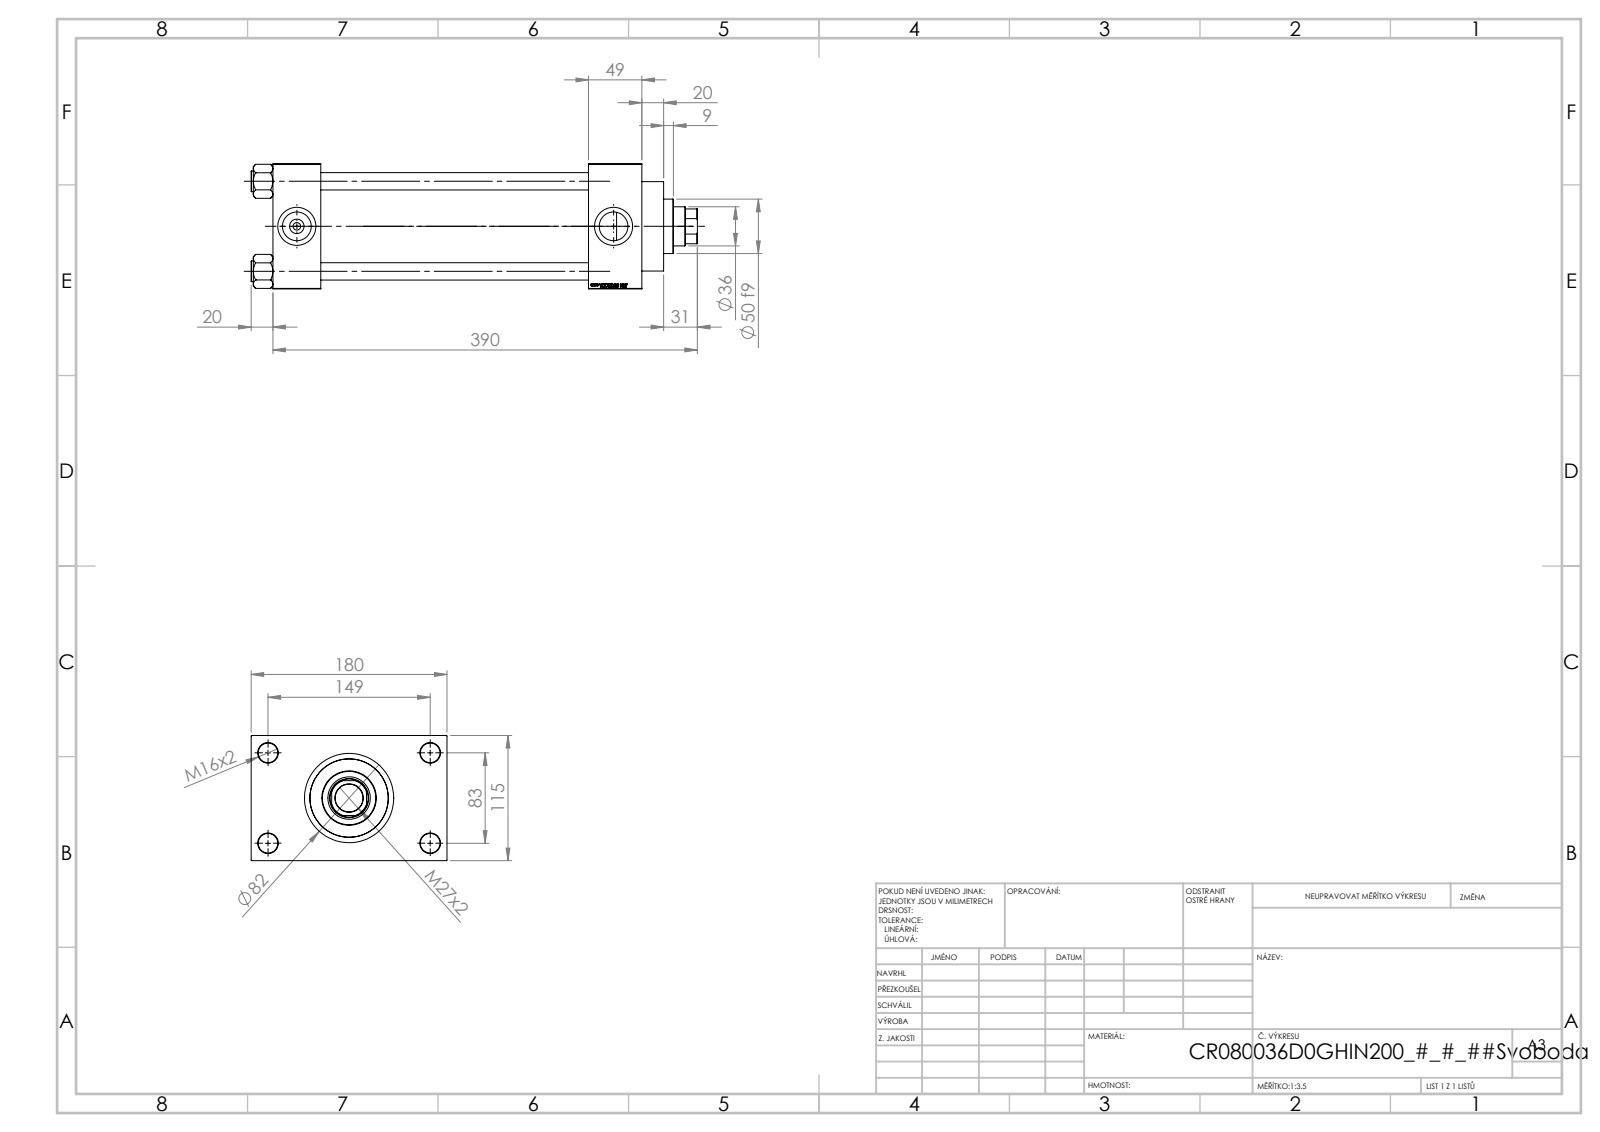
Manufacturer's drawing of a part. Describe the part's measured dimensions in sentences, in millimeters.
The part is named "V215_VC_A; V215CR_D_TYCINKA; NUT_M5_D; V215CR_D_Body (+1 more)". Its 3-D file was written by "SolidWorks 2019 (CONFIG_CONTROL_DESIGN)". It is 11 solids with 1151 faces: 545 planar, 88 cylindrical and 518 other. Overall it measures 410 by 180 by 115 millimeters. Its volume is 2 448 000 cubic millimeters and its surface area 447 014 square millimeters. Round holes: 4 of diameter 16, 4 of diameter 18, 2 of diameter 7, 2 of diameter 26.44, 2 of diameter 35, 1 of diameter 25.5, 1 of diameter 36, 1 of diameter 39, 1 of diameter 61, 1 of diameter 72, 1 of diameter 80. Round bosses or shafts: 4 of diameter 19, 1 of diameter 86, 1 of diameter 82, 1 of diameter 50. Partial cylindrical surfaces (rounded edges, fillets, slot ends): 1 of radius 17.5. The main face-to-face distances are 115, 246, 295, 49, 44, 290, 339, 32.5, 147.5, 180. The hole center spacings are 33.15, 58.48, 82.7, 85.28, 89.24, 115.85, 142.43, 83.
